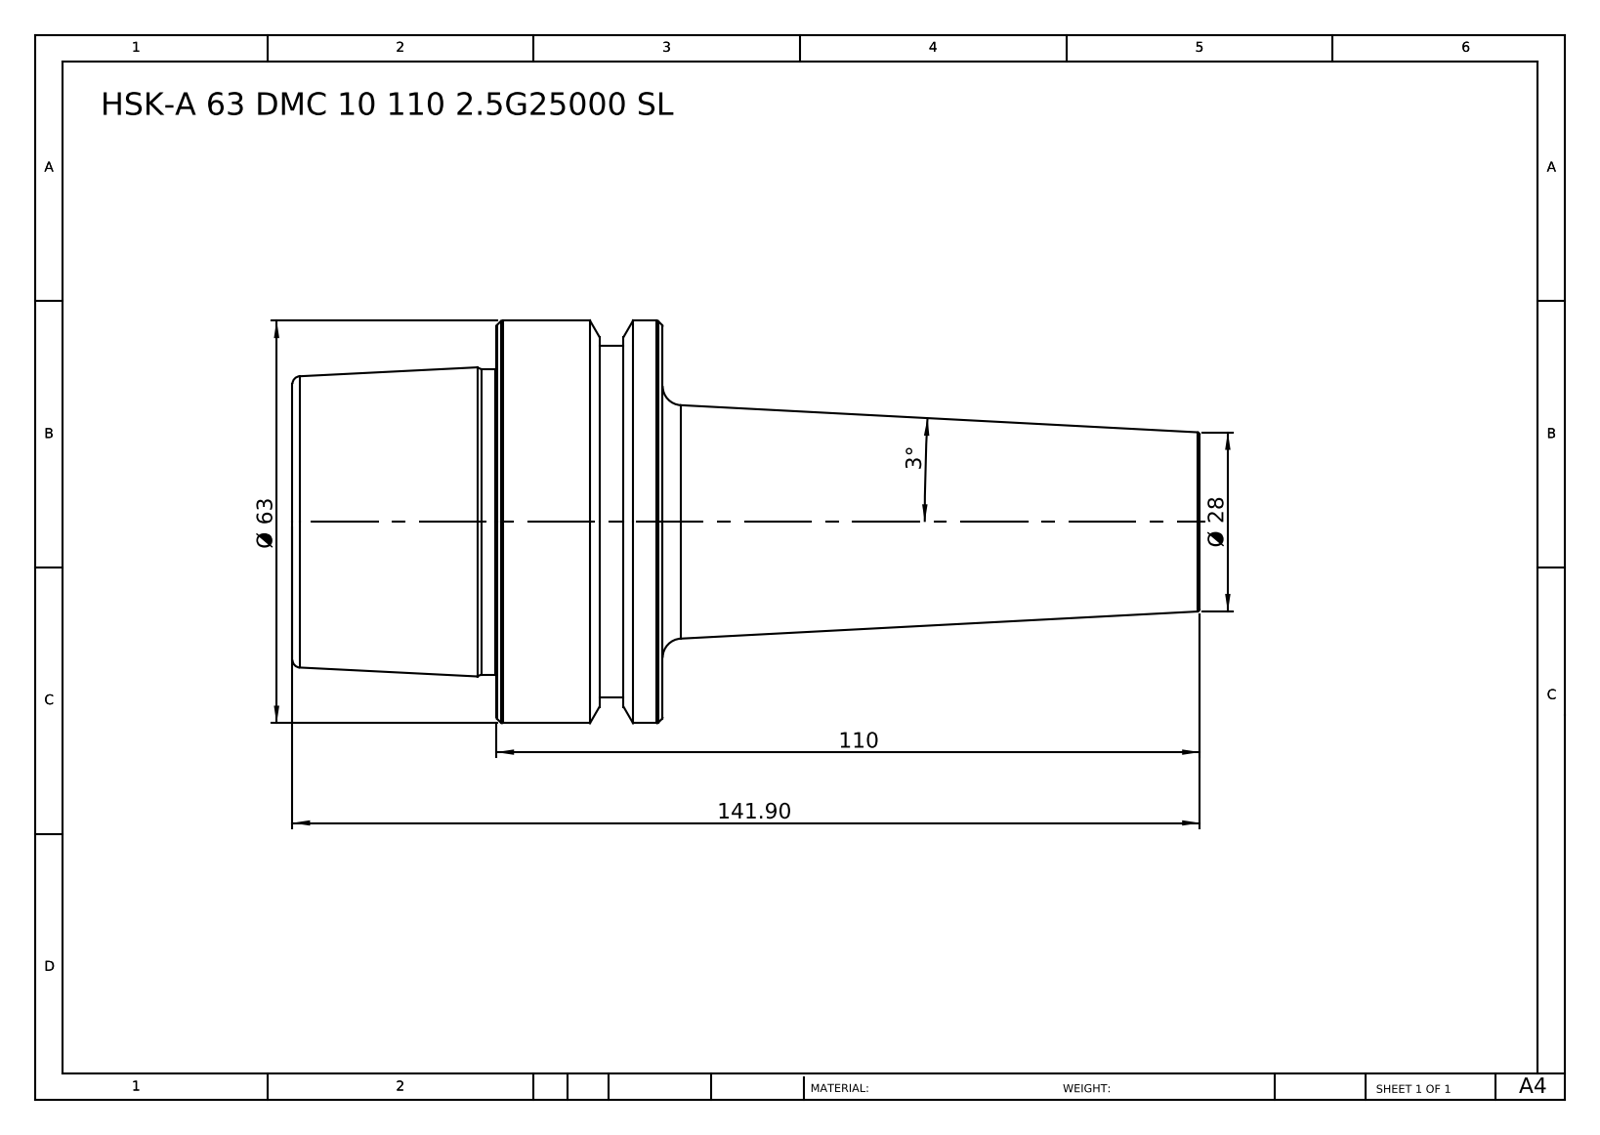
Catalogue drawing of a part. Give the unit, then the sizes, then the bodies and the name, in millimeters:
Units: millimetres
Overall size (bounding box): 141.9 × 63 × 63
Round bosses / shafts (diameter × count): ⌀63 ×1, ⌀55 ×1, ⌀47.78 ×1
Main face-to-face distances: 57.9, 26, 31.9, 84, 110, 141.9, 90.1, 6.1, 19.9, 51.8
Volume: 202 465 mm³ · Surface area: 24 620 mm²
Bodies: 1 solid, 46 faces (6 planar, 8 cylindrical, 32 other)
Part name (STEP PRODUCT): HSK-A 63 DMC 10 110 2.5G25000 SL
STEP written by: SolidWorks 2014 (CONFIG_CONTROL_DESIGN)
